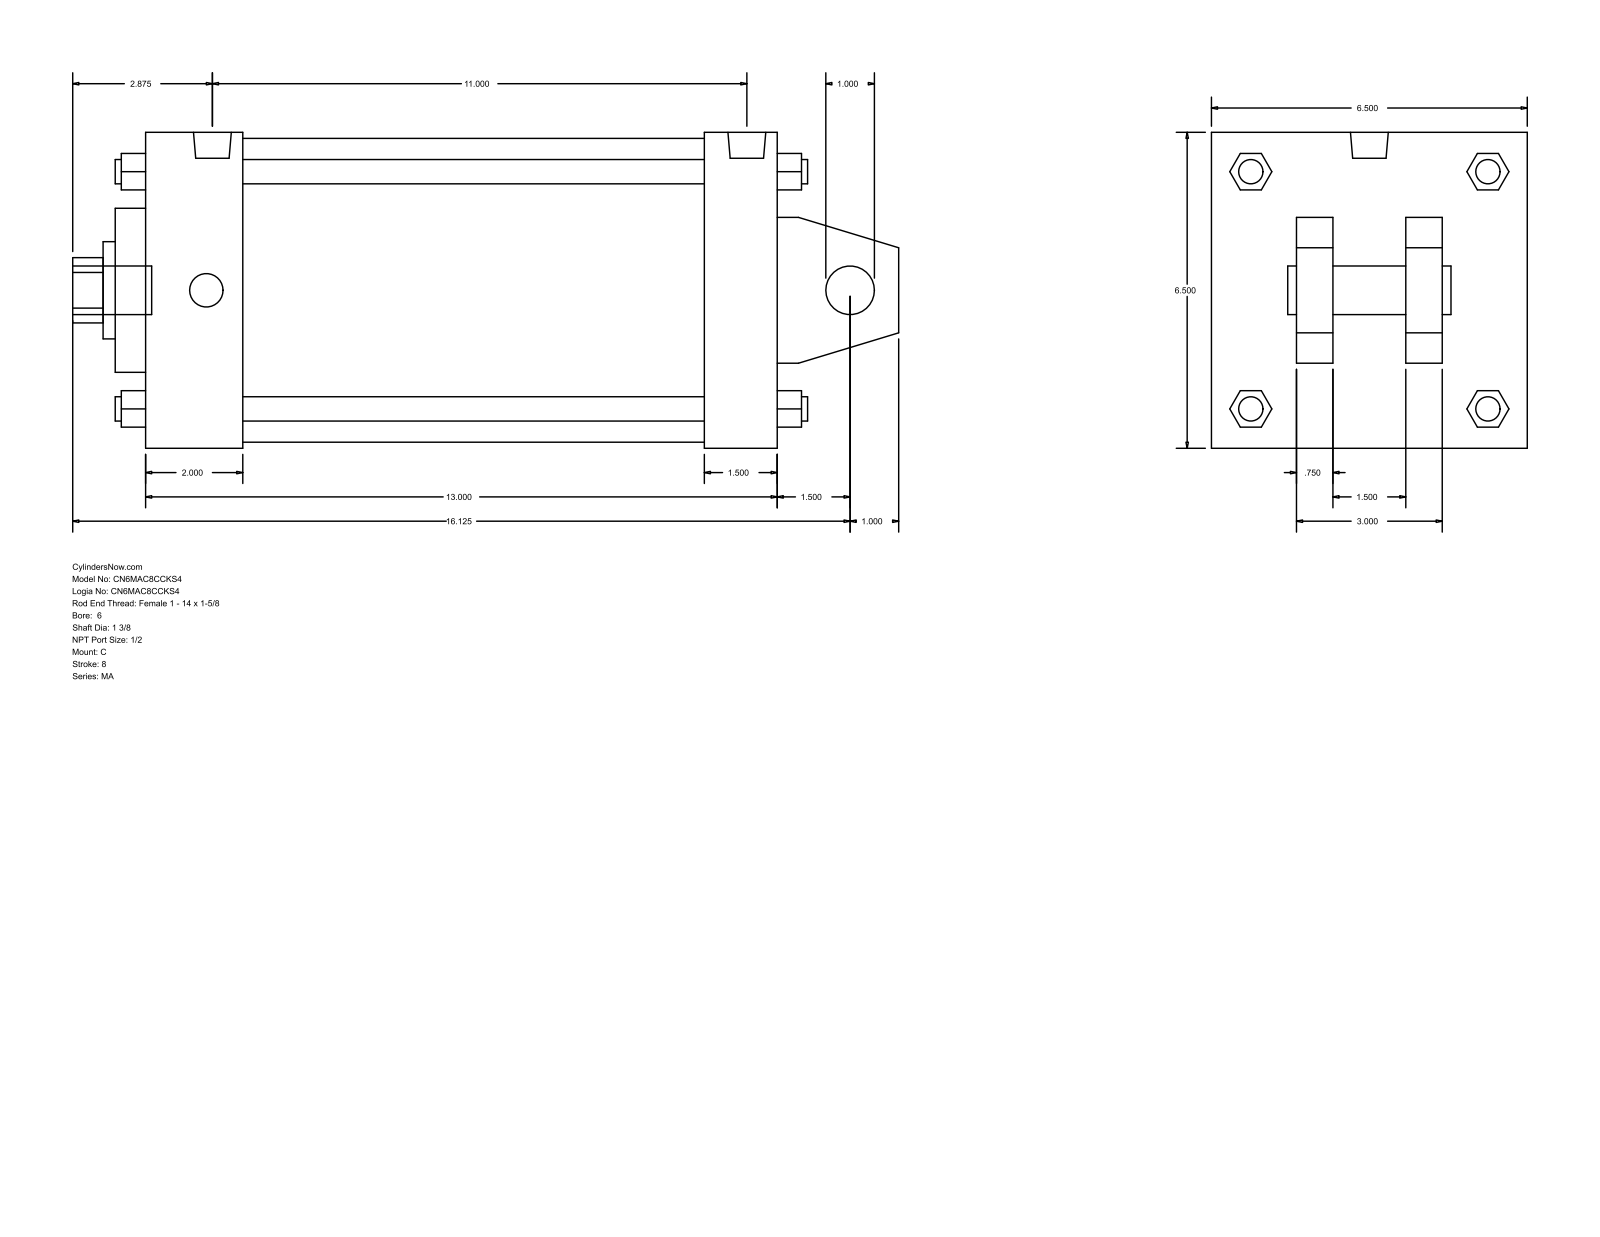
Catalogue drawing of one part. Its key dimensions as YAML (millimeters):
part_name: "MA_C__0600_1.375"
step_written_by: "GSSL Pune (CONFIG_CONTROL_DESIGN)"
units: millimeters
bodies: {solids: 0, faces: 141, planar: 109, cylindrical: 32, other: 0}
overall_size: [431.8, 165.1, 165.1]
round_holes:
  - {diameter: 25.4, count: 1}
  - {diameter: 34.92, count: 1}
  - {diameter: 50.8, count: 1}
  - {diameter: 85.72, count: 1}
  - {diameter: 158.75, count: 1}
round_bosses_or_shafts:
  - {diameter: 17.46, count: 4}
  - {diameter: 12.7, count: 4}
  - {diameter: 19.77, count: 2}
  - {diameter: 25.4, count: 1}
partial_cylinders:
  - {radius: 17.06, count: 1}
face_to_face_distances: [165.1, 330.2, 38.1, 19.05, 63.5, 101.6, 50.8, 44.45, 120.65, 292.1]
